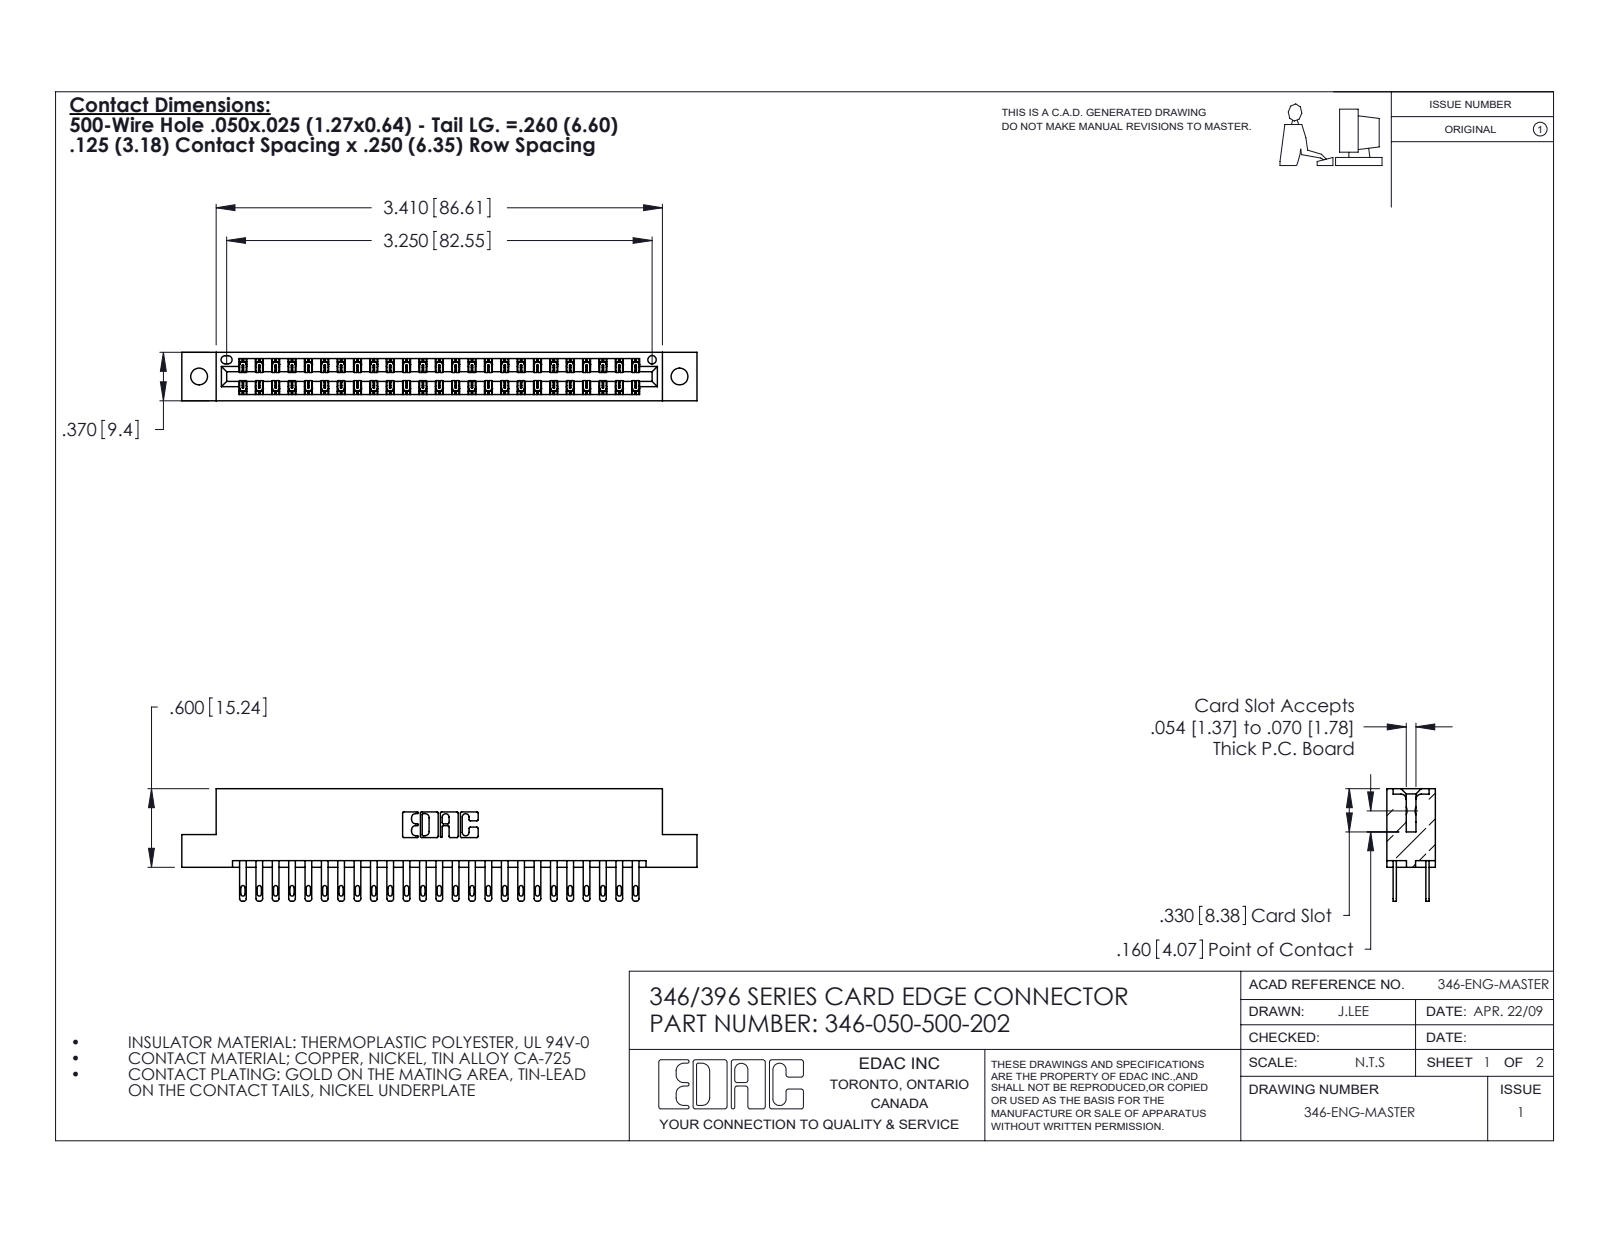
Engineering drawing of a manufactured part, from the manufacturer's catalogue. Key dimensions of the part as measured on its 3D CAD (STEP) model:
Part name (STEP PRODUCT): 346 Part_Flush Mounting Lugs - 0.128 Dia; 345-292-001_345-293-100; 346-050-500-202
STEP written by: SolidWorks 2020 (CONFIG_CONTROL_DESIGN)
Units: inches
Bodies: 51 solids, 2522 faces (1526 planar, 996 cylindrical, 0 other)
Overall size (bounding box): 3.935 × 0.86 × 0.37
Volume: 0.594 in³ · Surface area: 20.71 in²
Round holes (diameter × count): ⌀0.128 ×2, ⌀0.064 ×1
Partial cylindrical surfaces — rounded edges, fillets, slot ends (radius × count): R0.006 ×75, R0.016 ×50, R0.02 ×50, R0.01 ×22, R0.007 ×6, R0.031 ×6, R0.026 ×3, R0.014 ×2
Main face-to-face distances: 0.048, 0.322, 0.25, 0.37, 0.072, 0.298, 0.025, 0.275, 0.148, 0.222
Hole centre spacings: 0.246, 3.462, 3.67
